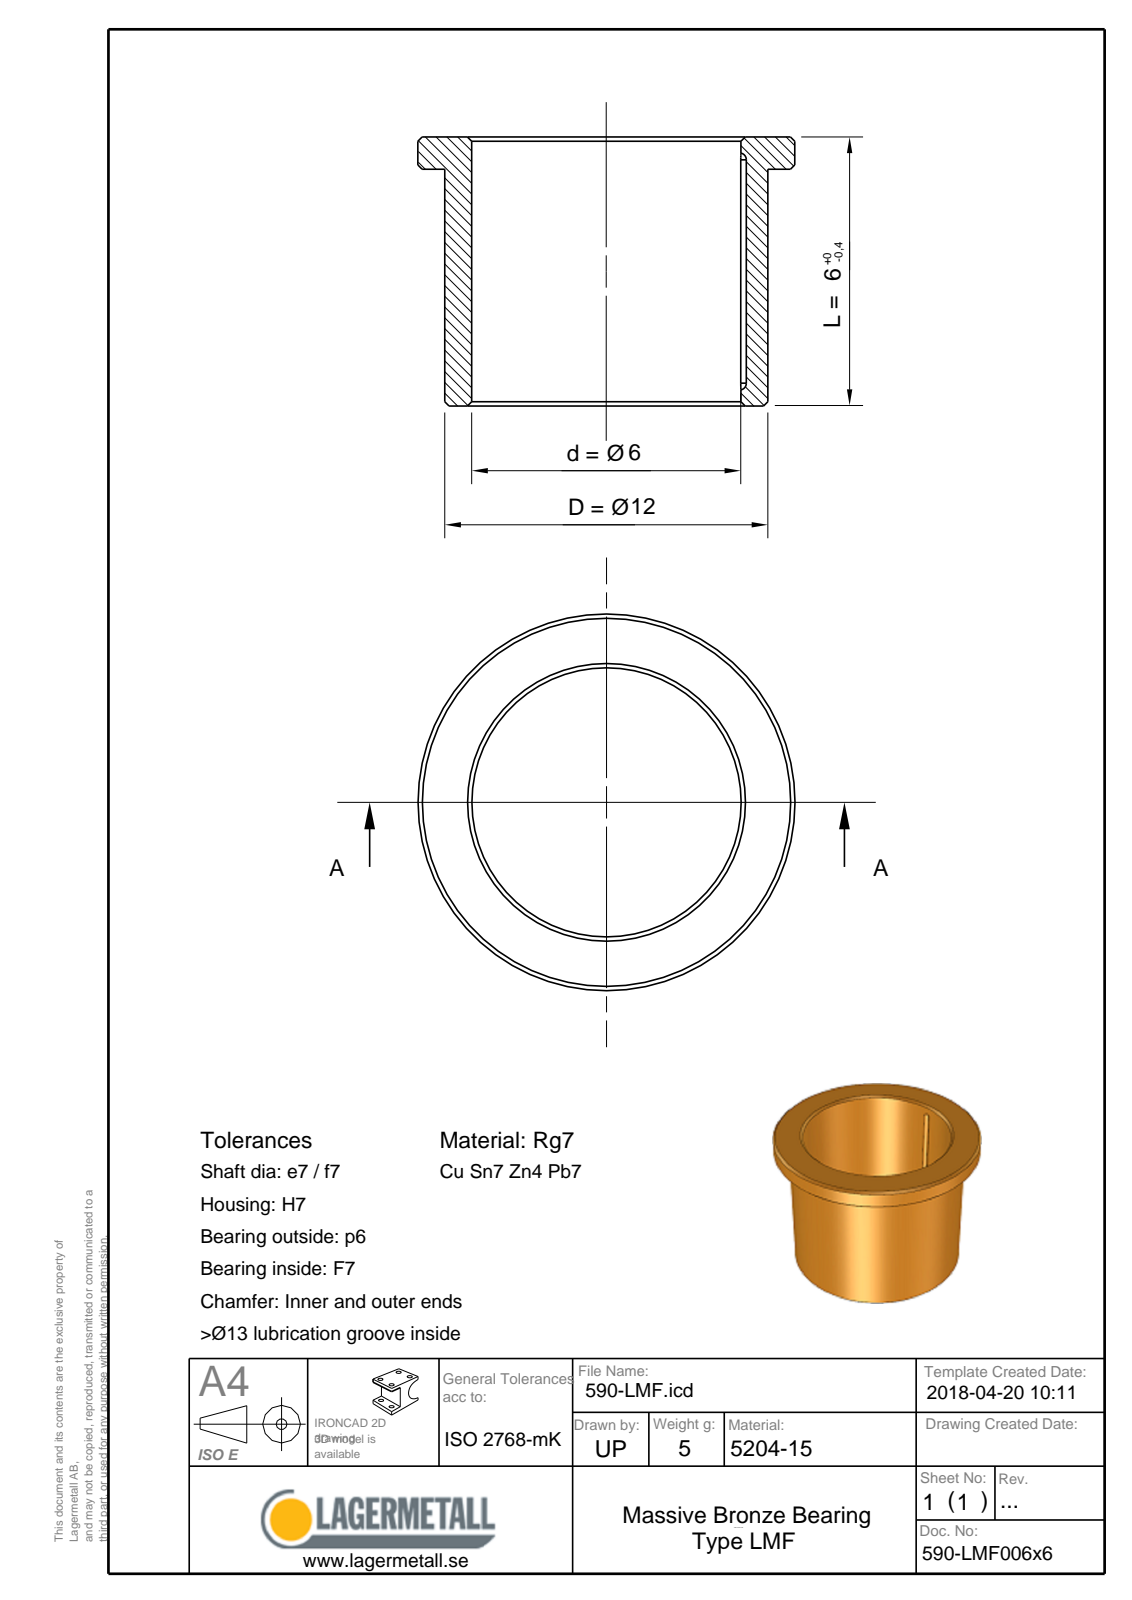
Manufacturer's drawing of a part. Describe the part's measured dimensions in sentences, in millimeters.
The part is named "590-LMF006x6". Its 3-D file was written by "Spatial InterOp 3D (CONFIG_CONTROL_DESIGN)". It is 1 solid with 11 faces: 3 planar, 3 cylindrical and 5 other. Overall it measures 14 by 14 by 6 millimeters. Its volume is 583 cubic millimeters and its surface area 574 square millimeters. Round holes: 1 of diameter 6. Round bosses or shafts: 1 of diameter 14, 1 of diameter 12. The main face-to-face distances are 6, 4, 2.
